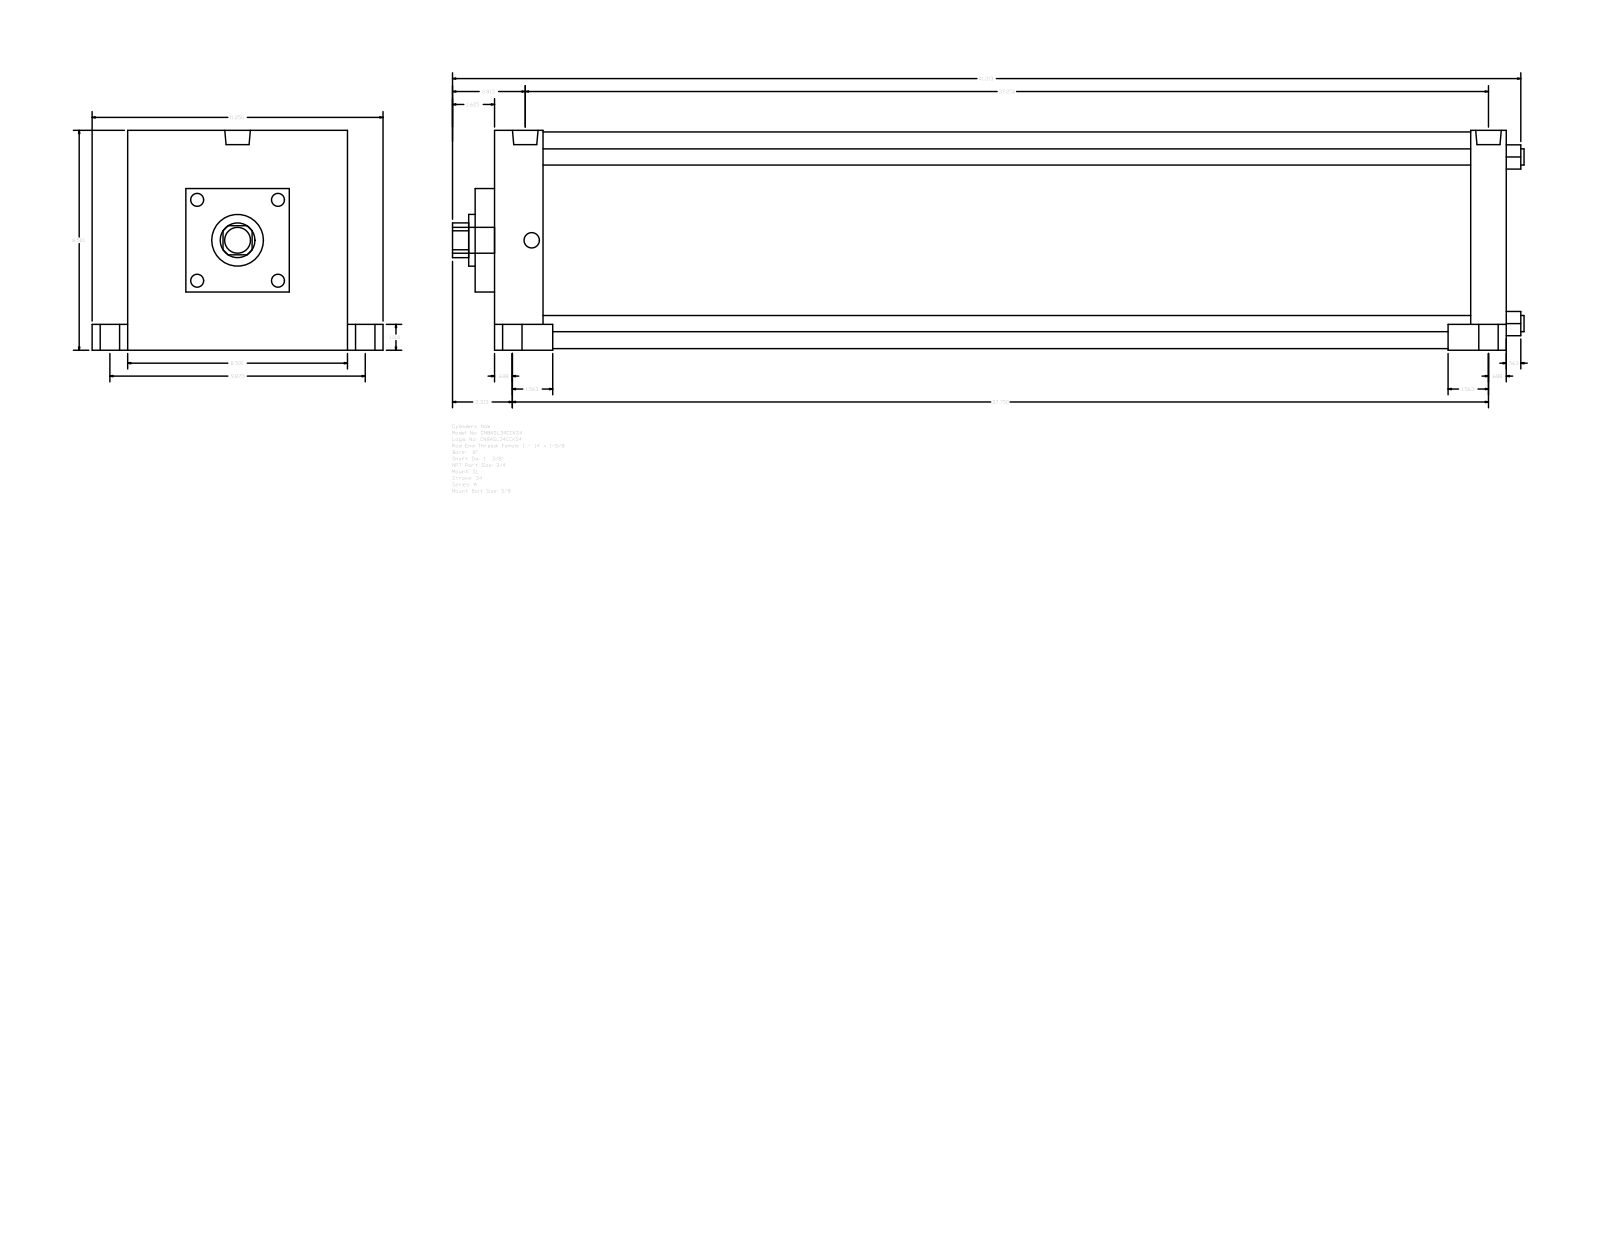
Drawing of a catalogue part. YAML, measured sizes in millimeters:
part_name: "A_SL__0800_1.375"
step_written_by: "GSSL Pune (CONFIG_CONTROL_DESIGN)"
units: millimeters
bodies: {solids: 0, faces: 117, planar: 85, cylindrical: 32, other: 0}
overall_size: [1052.51, 285.75, 215.9]
round_holes:
  - {diameter: 15.88, count: 4}
  - {diameter: 34.92, count: 1}
  - {diameter: 50.8, count: 1}
  - {diameter: 212.72, count: 1}
round_bosses_or_shafts:
  - {diameter: 25.4, count: 5}
  - {diameter: 19.05, count: 4}
  - {diameter: 15.08, count: 4}
  - {diameter: 25.12, count: 2}
partial_cylinders:
  - {radius: 17.06, count: 1}
face_to_face_distances: [993.78, 215.9, 34.93, 57.15, 47.63, 946.15, 958.85, 911.22, 19.04, 66.67]
hole_center_spacings: [115.67, 163.58, 231.34]
